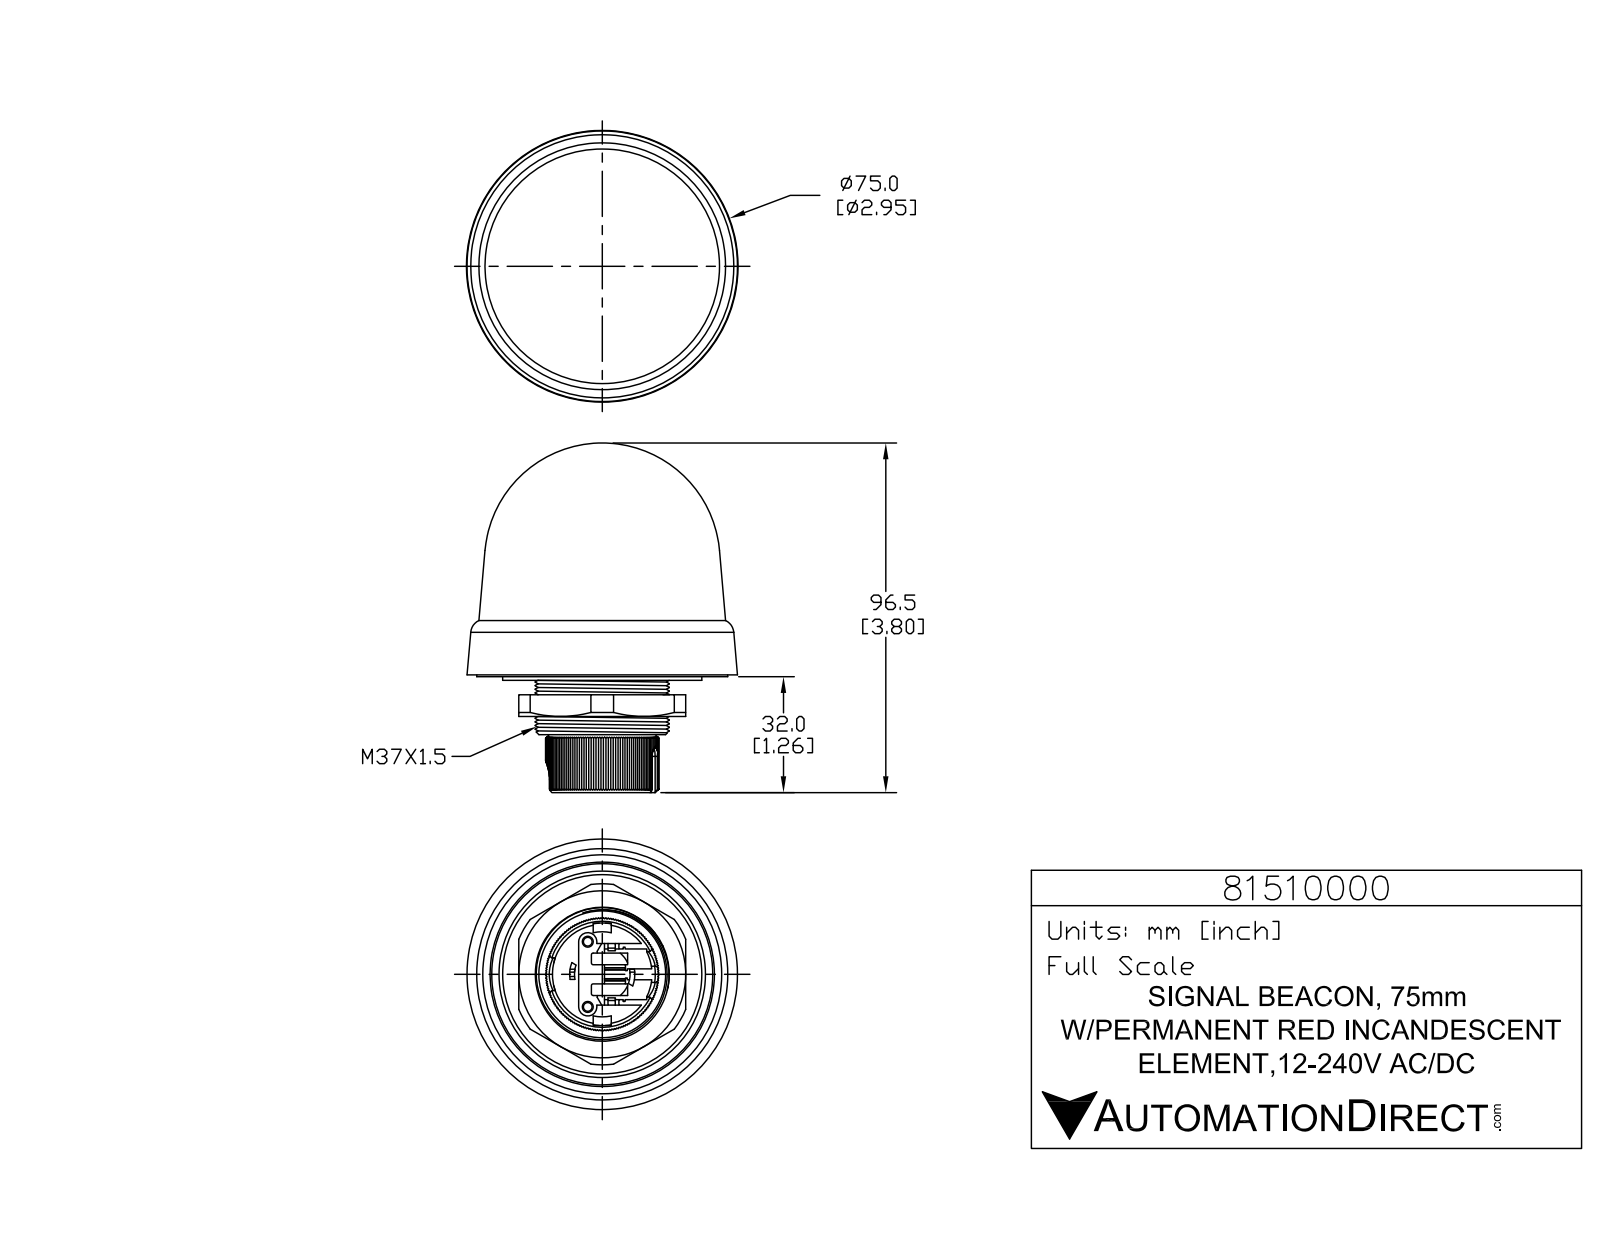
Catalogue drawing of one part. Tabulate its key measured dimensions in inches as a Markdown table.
| quantity | value |
| --- | --- |
| part name | 81510000 |
| STEP written by | SolidWorks 2019 (CONFIG_CONTROL_DESIGN) |
| units | inches |
| bodies | 3 solids, 560 faces (432 planar, 80 cylindrical, 48 other) |
| overall size | 3.799 × 2.941 × 2.941 |
| volume | 12.36 in³ |
| surface area | 58.68 in² |
| round holes (diameter × count) | 0.094 × 2, 0.118 × 2, 0.604 × 1, 1.142 × 1 |
| round bosses / shafts (diameter × count) | 0.217 × 2, 0.067 × 2, 2.165 × 1, 1.457 × 1, 0.925 × 1 |
| partial cylindrical surfaces (radius × count) | 0.008 × 6, 0.039 × 6, 0.02 × 4, 0.031 × 2, 0.079 × 2, 0.098 × 2, 0.177 × 1, 0.354 × 1 |
| main face-to-face distances | 0.177, 0.354, 0.197, 0.433, 0.512, 0.335, 0.059, 0.394, 0.118, 0.157 |
| hole center spacings | 0.388, 0.709 |
